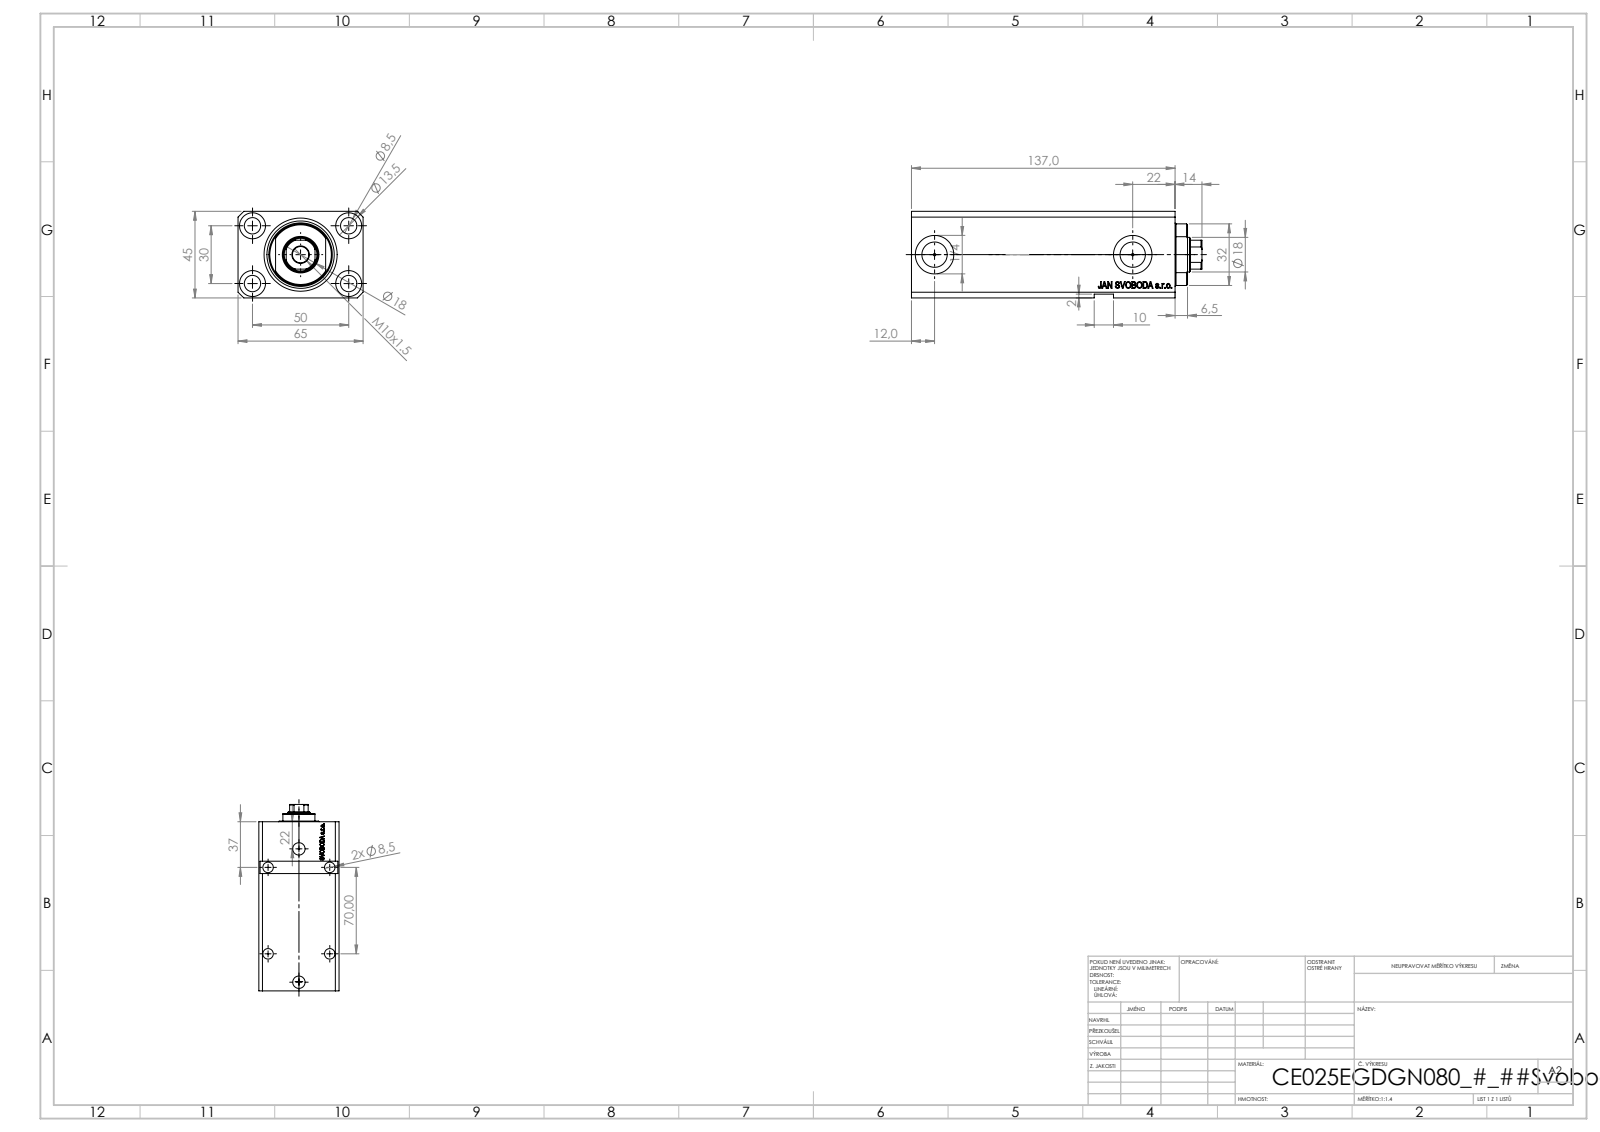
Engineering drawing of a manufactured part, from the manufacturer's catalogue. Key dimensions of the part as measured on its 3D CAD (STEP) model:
Part name (STEP PRODUCT): V250CE_C_VCP; V250CE_VC_E; V250CE_E_Body
STEP written by: SolidWorks 2019 (CONFIG_CONTROL_DESIGN)
Units: millimetres
Bodies: 3 solids, 933 faces (439 planar, 116 cylindrical, 378 other)
Overall size (bounding box): 151 × 65 × 45
Volume: 331 245 mm³ · Surface area: 81 708 mm²
Round holes (diameter × count): ⌀8.5 ×9, ⌀1.25 ×4, ⌀13.5 ×4, ⌀10 ×2, ⌀13.16 ×2, ⌀20 ×2, ⌀18 ×1, ⌀25 ×1, ⌀38 ×1
Partial cylindrical surfaces — rounded edges, fillets, slot ends (radius × count): R8.5 ×1, R16 ×1
Main face-to-face distances: 45, 65, 123, 14, 137, 6.9, 116.1, 130.1, 43, 64.9
Hole centre spacings: 29.15, 50, 30, 33.61, 33.97, 58.31, 70, 86.02
